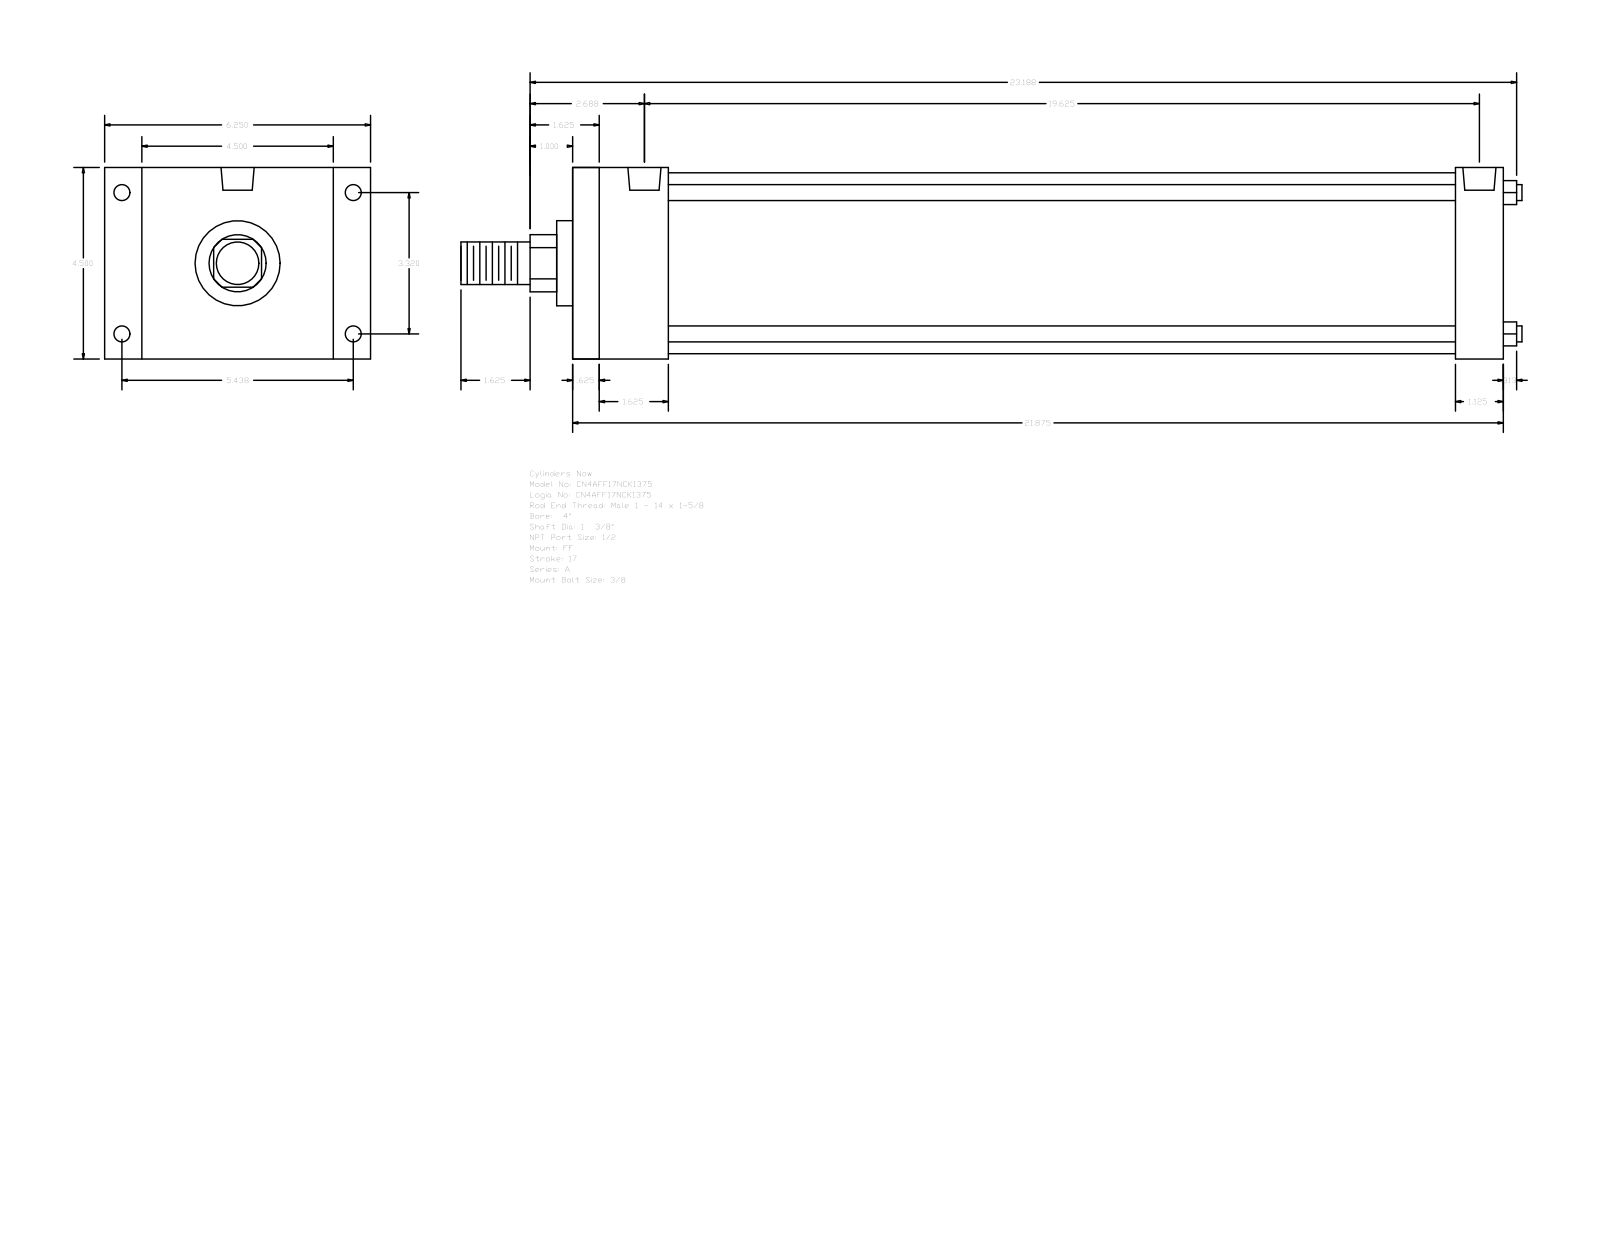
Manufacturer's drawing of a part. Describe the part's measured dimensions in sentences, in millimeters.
The part is named "A_FF__0400_1.375". Its 3-D file was written by "GSSL Pune (CONFIG_CONTROL_DESIGN)". It is 0 solids with 92 faces: 64 planar, 28 cylindrical and 0 other. Overall it measures 633.41 by 158.75 by 114.3 millimeters. Round holes: 4 of diameter 8.73, 4 of diameter 9.53, 2 of diameter 19.77. Round bosses or shafts: 4 of diameter 9.53, 1 of diameter 107.95, 1 of diameter 50.8, 1 of diameter 34.92, 1 of diameter 25.4. Partial cylindrical surfaces (rounded edges, fillets, slot ends): 1 of radius 17.06. The main face-to-face distances are 114.3, 555.62, 539.75, 15.87, 57.15, 28.57, 22.23, 136.53, 527.05, 511.18. The hole center spacings are 3.18, 84.32, 138.12, 161.82, 492.12, 495.3, 498.48.
